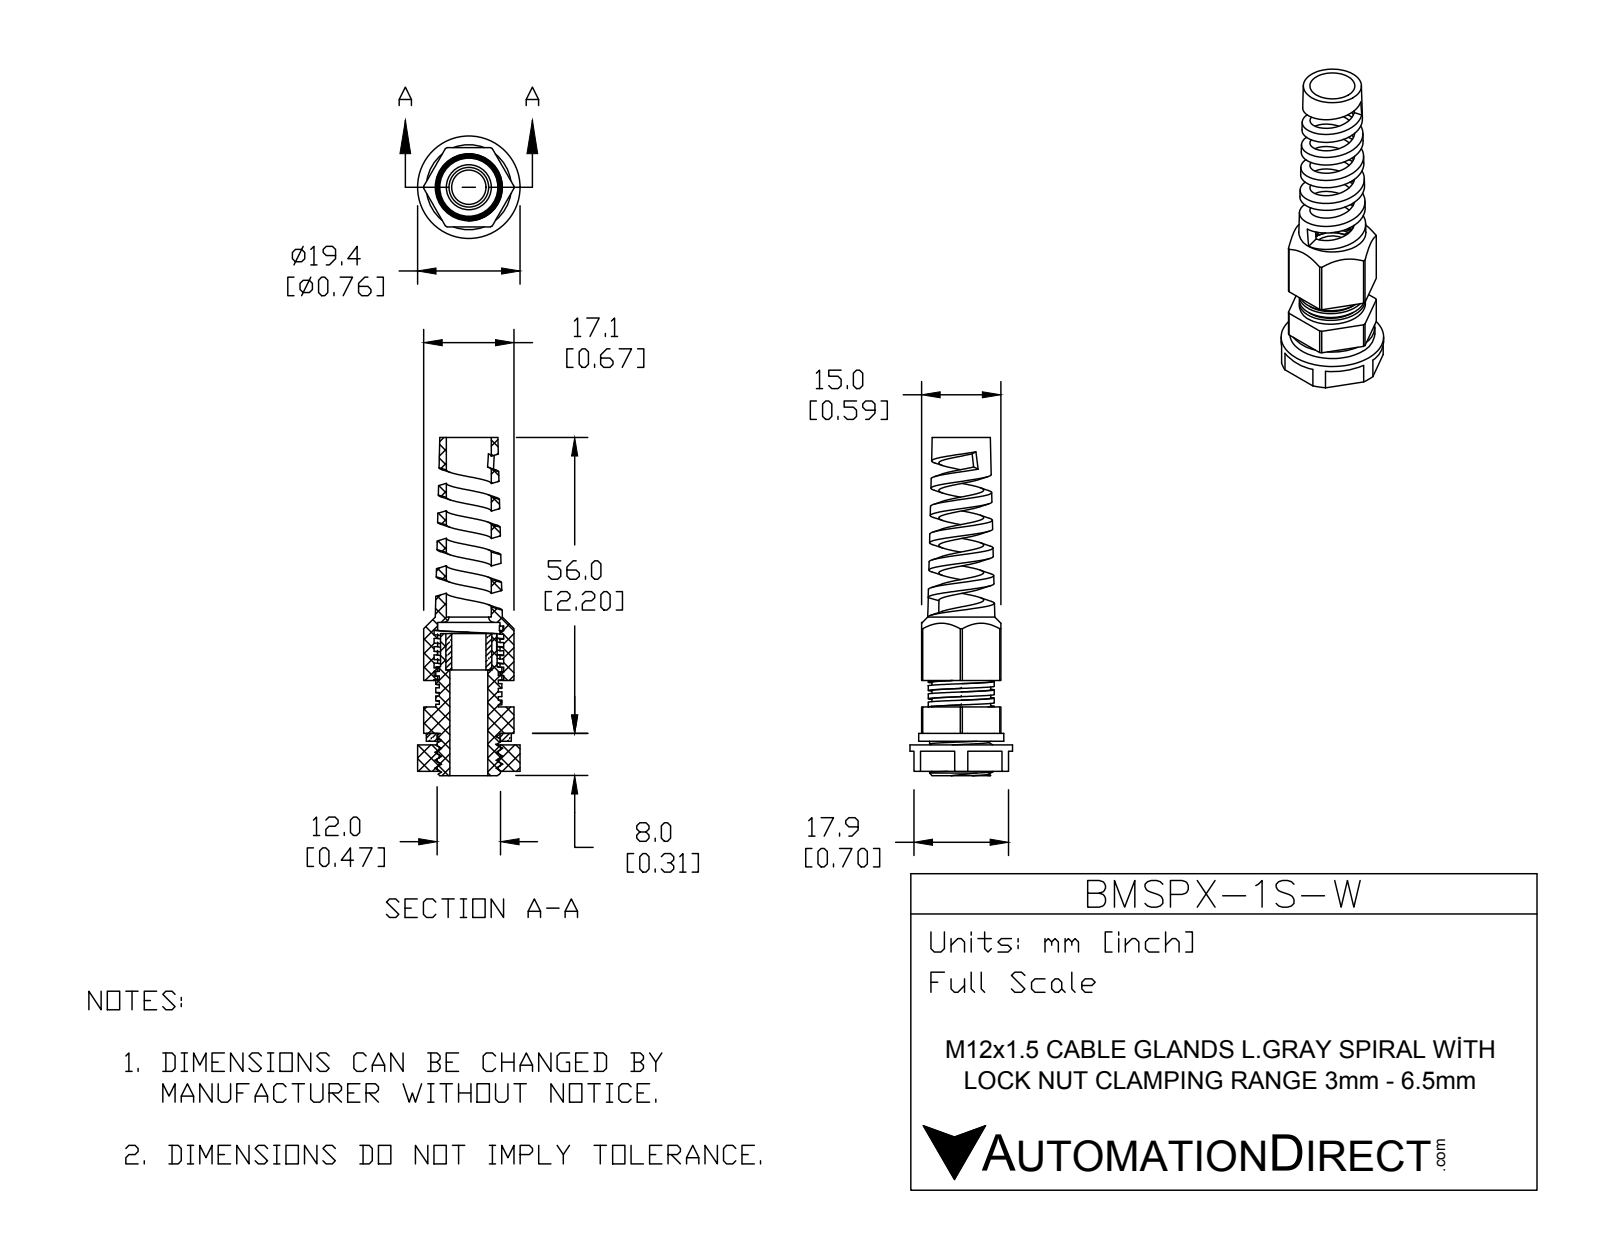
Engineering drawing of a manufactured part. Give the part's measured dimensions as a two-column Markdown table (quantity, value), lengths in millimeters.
| quantity | value |
| --- | --- |
| part name | BMSPX-1S-W |
| STEP written by | SolidWorks 2015 (CONFIG_CONTROL_DESIGN) |
| units | millimeters |
| bodies | 5 solids, 224 faces (102 planar, 89 cylindrical, 33 other) |
| overall size | 64 × 19.4 × 19.4 |
| volume | 4 942 mm³ |
| surface area | 7 467 mm² |
| round holes (diameter × count) | 6.5 × 1, 7.2 × 1, 8.5 × 1, 8.7 × 1, 11.18 × 1, 11.8 × 1, 11.83 × 1 |
| round bosses / shafts (diameter × count) | 19.4 × 1, 16.1 × 1, 12.5 × 1, 12 × 1, 10.7 × 1 |
| partial cylindrical surfaces (radius × count) | 8.55 × 1 |
| main face-to-face distances | 15, 5, 7.18, 2.18, 1.45, 16.45, 12.18, 6.5, 5.68, 0.68 |
